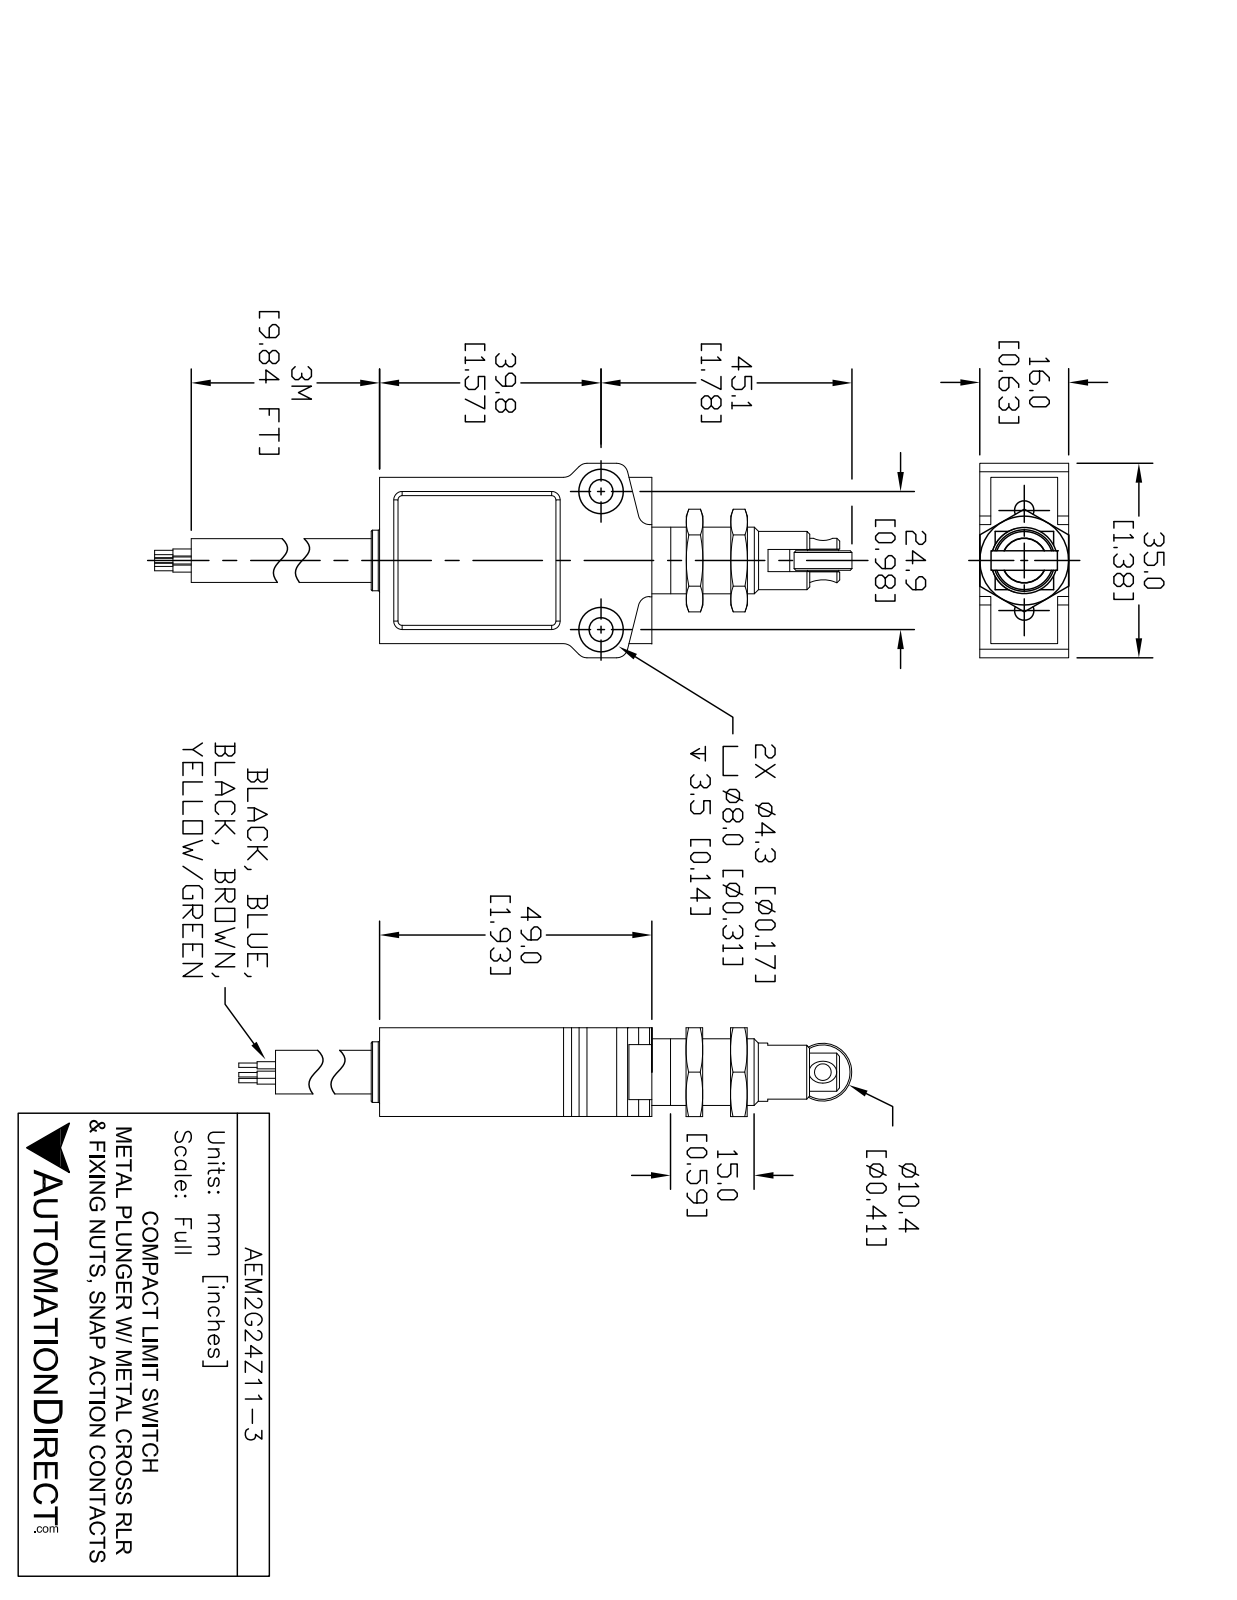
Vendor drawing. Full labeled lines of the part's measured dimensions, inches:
Part name (STEP PRODUCT): AEM2G24Z11-3_Default
STEP written by: SolidWorks 2021 (CONFIG_CONTROL_DESIGN)
Units: inches
Bodies: 2 solids, 191 faces (98 planar, 47 cylindrical, 46 other)
Overall size (bounding box): 3.965 × 1.38 × 0.63
Volume: 1.565 in³ · Surface area: 14.03 in²
Round holes (diameter × count): ⌀0.177 ×2, ⌀0.344 ×2
Round bosses / shafts (diameter × count): ⌀0.05 ×5, ⌀0.031 ×5, ⌀0.41 ×2, ⌀0.47 ×1, ⌀0.43 ×1, ⌀0.31 ×1
Partial cylindrical surfaces — rounded edges, fillets, slot ends (radius × count): R0.03 ×8, R0.08 ×8, R0.135 ×1
Main face-to-face distances: 0.03, 0.6, 0.57, 0.63, 1.18, 0.12, 0.3, 1.93, 0.187, 0.443
Hole centre spacings: 0.98
